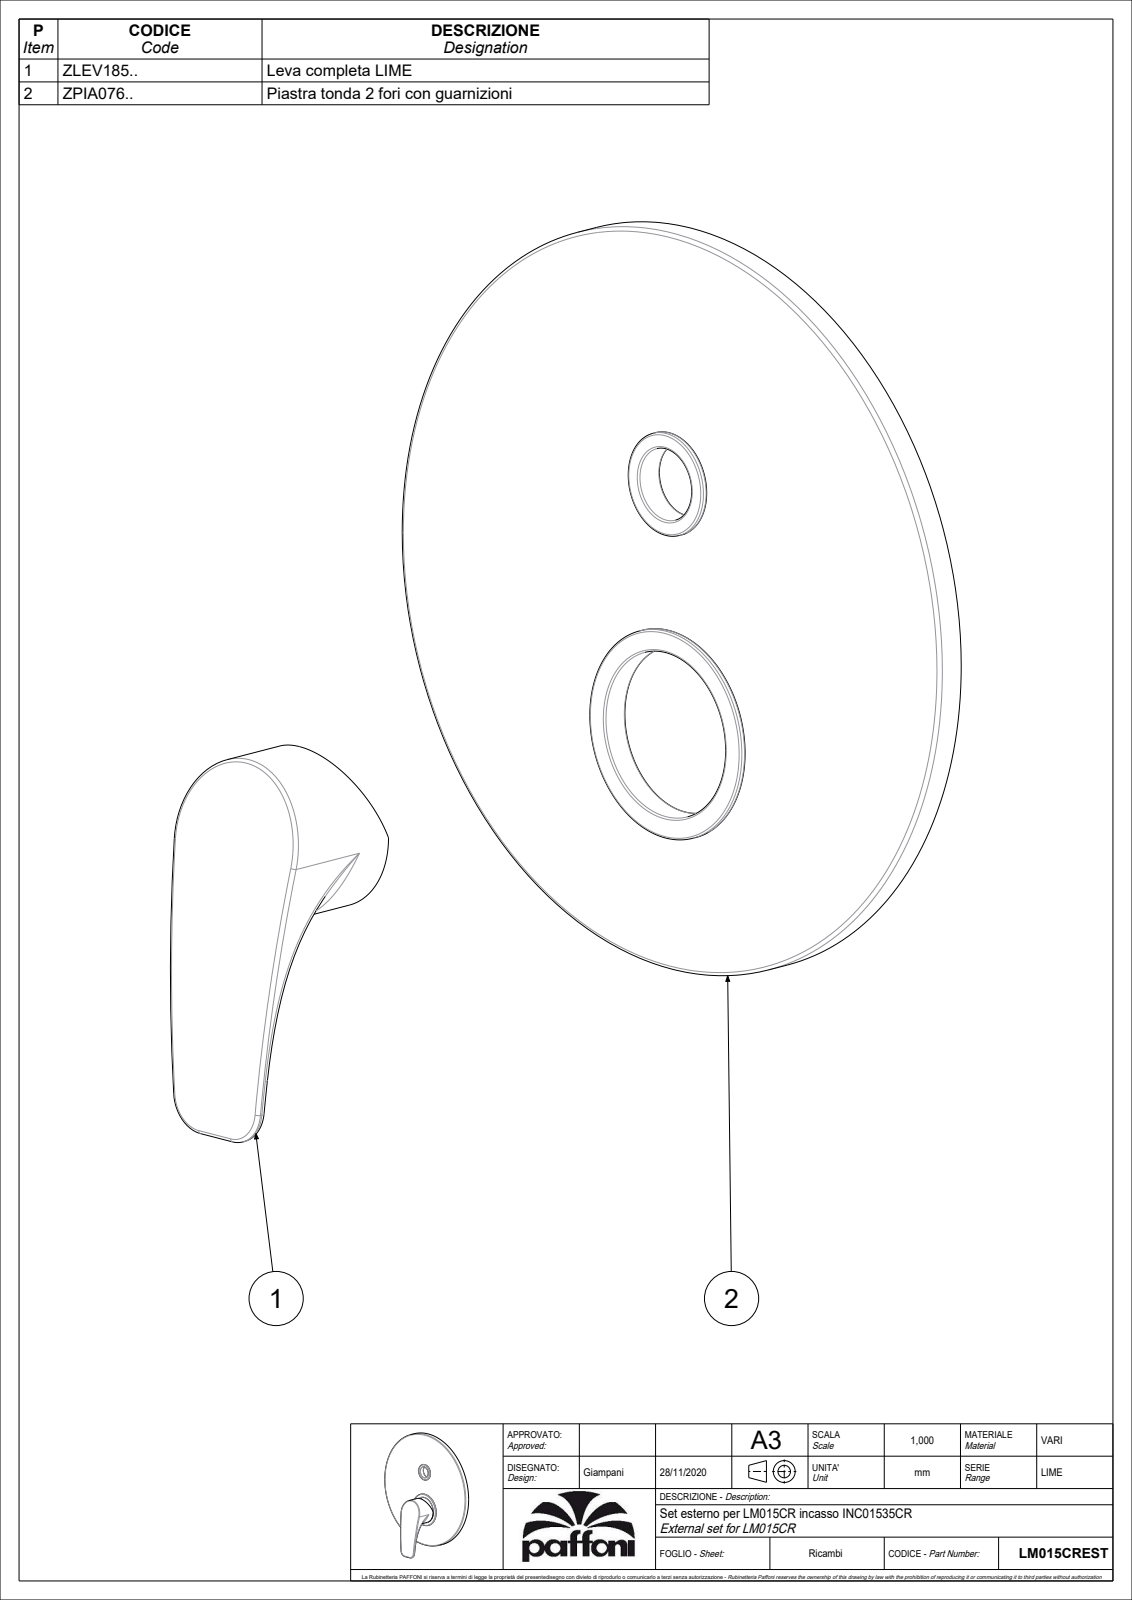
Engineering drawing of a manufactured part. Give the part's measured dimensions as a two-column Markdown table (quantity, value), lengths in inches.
| quantity | value |
| --- | --- |
| part name | LM015CREST |
| STEP written by | CREO PARAMETRIC BY PTC INC, 2020044 (CONFIG_CONTROL_DESIGN) |
| units | inches |
| bodies | 2 solids, 186 faces (56 planar, 60 cylindrical, 70 other) |
| overall size | 8.417 × 7.874 × 2.087 |
| volume | 10.47 in³ |
| surface area | 150.9 in² |
| round holes (diameter × count) | 0.118 × 1, 0.165 × 1, 0.752 × 1, 1.756 × 1, 1.969 × 1, 5.709 × 1, 7.795 × 1 |
| round bosses / shafts (diameter × count) | 7.874 × 1, 7.677 × 1, 2.213 × 1, 1.965 × 1, 1.772 × 1, 0.988 × 1, 0.925 × 1, 0.299 × 1 |
| partial cylindrical surfaces (radius × count) | 0.039 × 12, 0.394 × 2, 0.079 × 1, 13.957 × 1, 16.687 × 1, 16.805 × 1 |
| main face-to-face distances | 0.039, 0.315, 0.354, 0.079, 0.118, 0.433, 0.394, 0.276, 0.358, 0.126 |
| hole center spacings | 1.268, 1.409, 2.677 |
